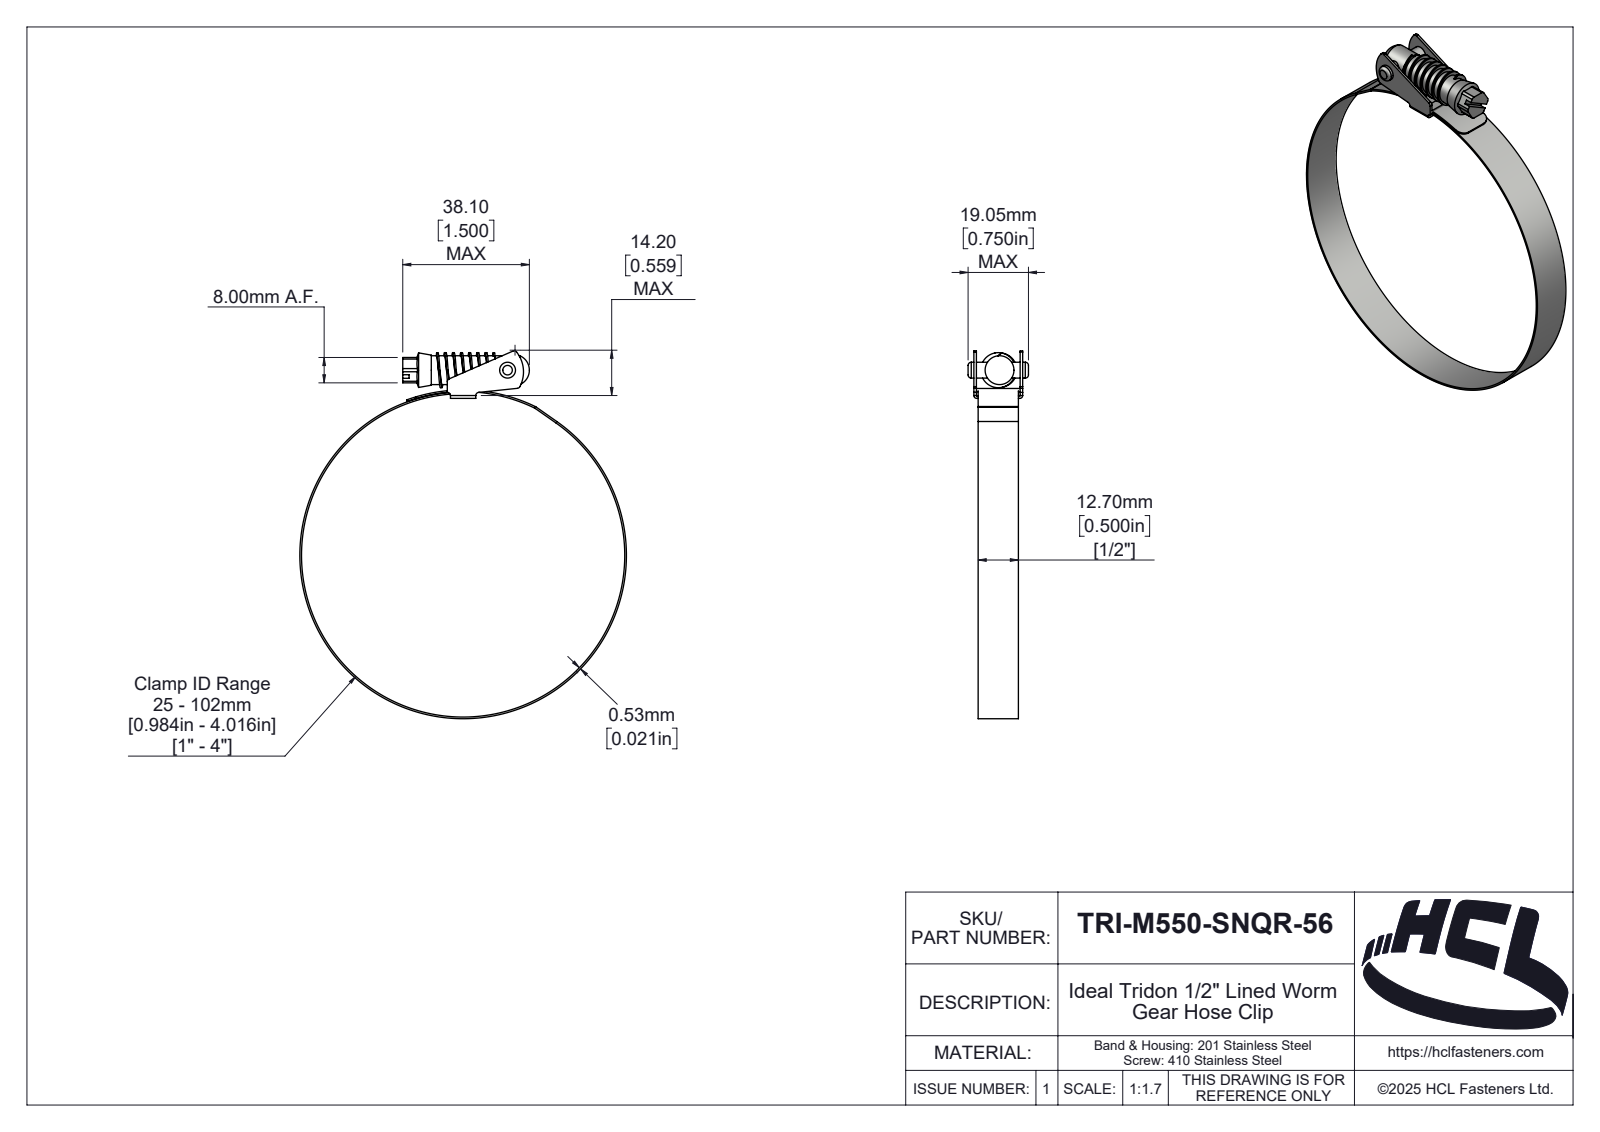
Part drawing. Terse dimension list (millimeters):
name: TRI-M550-SNQR-56
written by: SolidWorks 2025 (AUTOMOTIVE_DESIGN)
unit: mm
bodies: 5 solids, 222 faces (44 planar, 112 cylindrical, 66 other)
size: 116.02 × 103.06 × 19.05
volume: 5 470 mm³; area: 12 593 mm²
holes: 1× ⌀5, 1× ⌀102
bosses: 1× ⌀103.06, 1× ⌀9.1
rounds: 11× R1, 2× R0.1, 2× R0.9, 2× R3, 1× R0.46, 1× R1.89, 1× R2, 1× R2.35
face distances: 0.8, 14.6, 1.35, 14.05, 0.55, 13.25, 15.4, 13.8, 12.7, 1
hole spacings: 60.06
